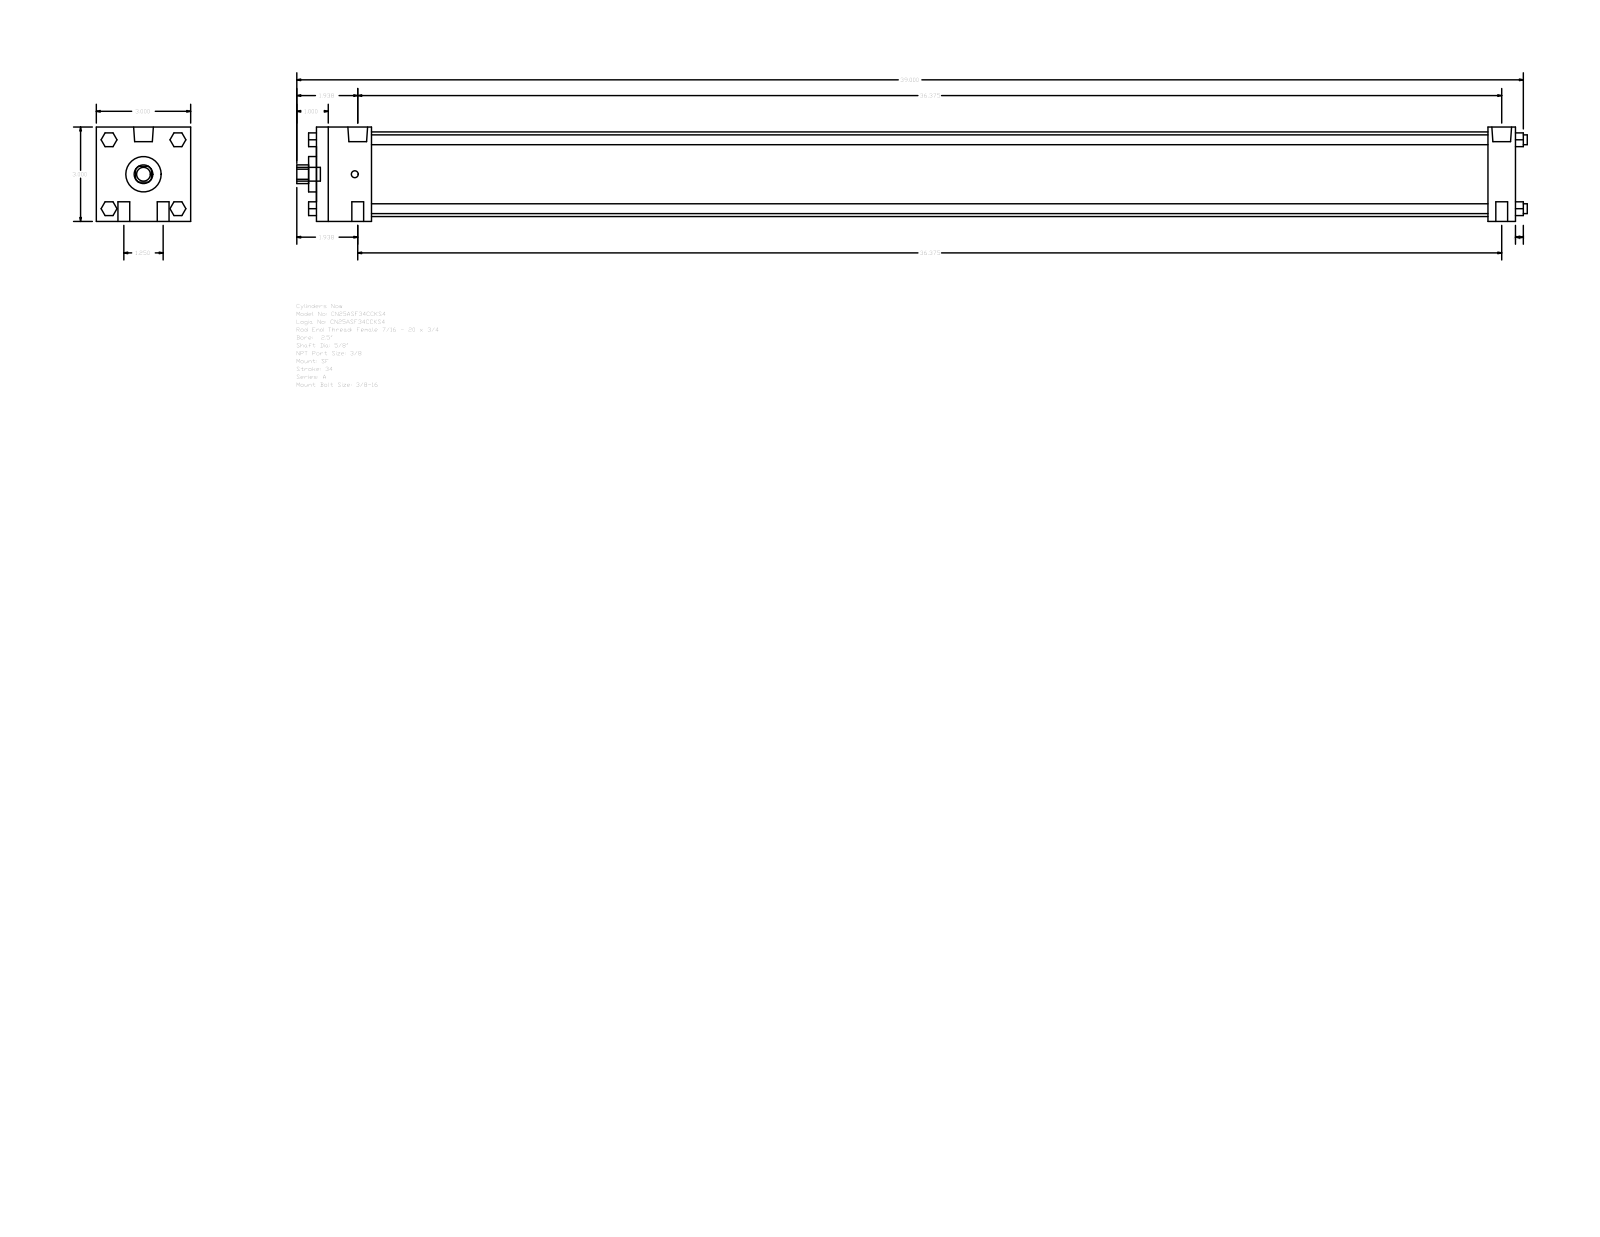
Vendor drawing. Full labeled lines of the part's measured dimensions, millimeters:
Part name (STEP PRODUCT): A_SF__0250_0.625
STEP written by: GSSL Pune (CONFIG_CONTROL_DESIGN)
Units: millimetres
Bodies: 0 solids, 124 faces (94 planar, 30 cylindrical, 0 other)
Overall size (bounding box): 993.77 × 76.2 × 76.2
Round holes (diameter × count): ⌀15.88 ×1, ⌀28.57 ×1, ⌀68.33 ×1
Round bosses / shafts (diameter × count): ⌀9.53 ×4, ⌀7.94 ×4, ⌀15.93 ×2, ⌀5.56 ×2, ⌀11.11 ×1
Partial cylindrical surfaces — rounded edges, fillets, slot ends (radius × count): R7.54 ×1
Main face-to-face distances: 76.2, 968.37, 44.45, 946.14, 22.23, 901.69, 923.92, 974.72, 6.35, 50.8
